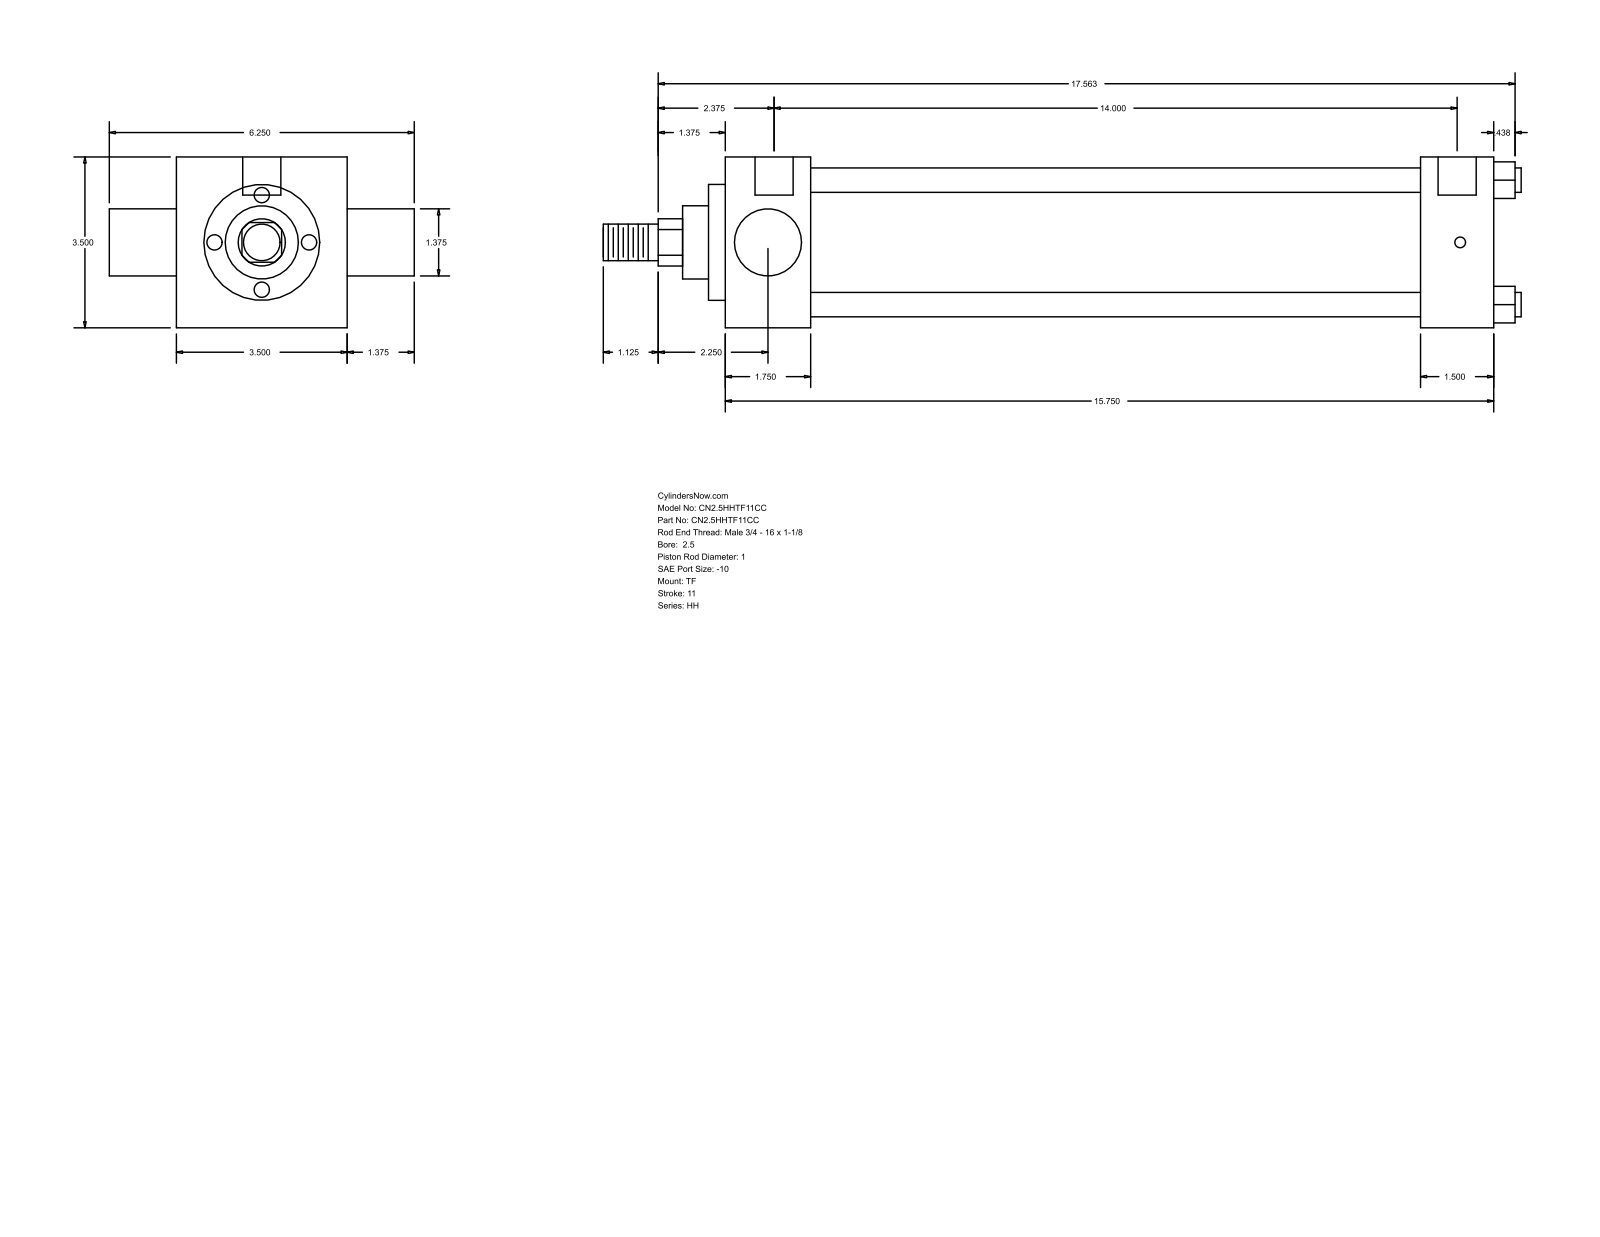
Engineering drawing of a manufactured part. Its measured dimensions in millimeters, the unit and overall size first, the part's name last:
Units: millimetres
Overall size (bounding box): 477.84 × 158.75 × 88.9
Round holes (diameter × count): ⌀5.56 ×3, ⌀19.84 ×2
Round bosses / shafts (diameter × count): ⌀12.7 ×4, ⌀73.03 ×1, ⌀60.33 ×1, ⌀38.1 ×1, ⌀34.92 ×1, ⌀25.4 ×1, ⌀19.05 ×1
Partial cylindrical surfaces — rounded edges, fillets, slot ends (radius × count): R12.29 ×1
Main face-to-face distances: 88.9, 400.06, 38.1, 44.46, 355.6, 361.96, 317.5, 34.93, 123.83, 8.73
Hole centre spacings: 1.58, 1.59, 355.6, 357.18, 357.19, 358.77
Bodies: 0 solids, 86 faces (61 planar, 25 cylindrical, 0 other)
Part name (STEP PRODUCT): HH_TF__0250_1
STEP written by: GSSL Pune (CONFIG_CONTROL_DESIGN)
